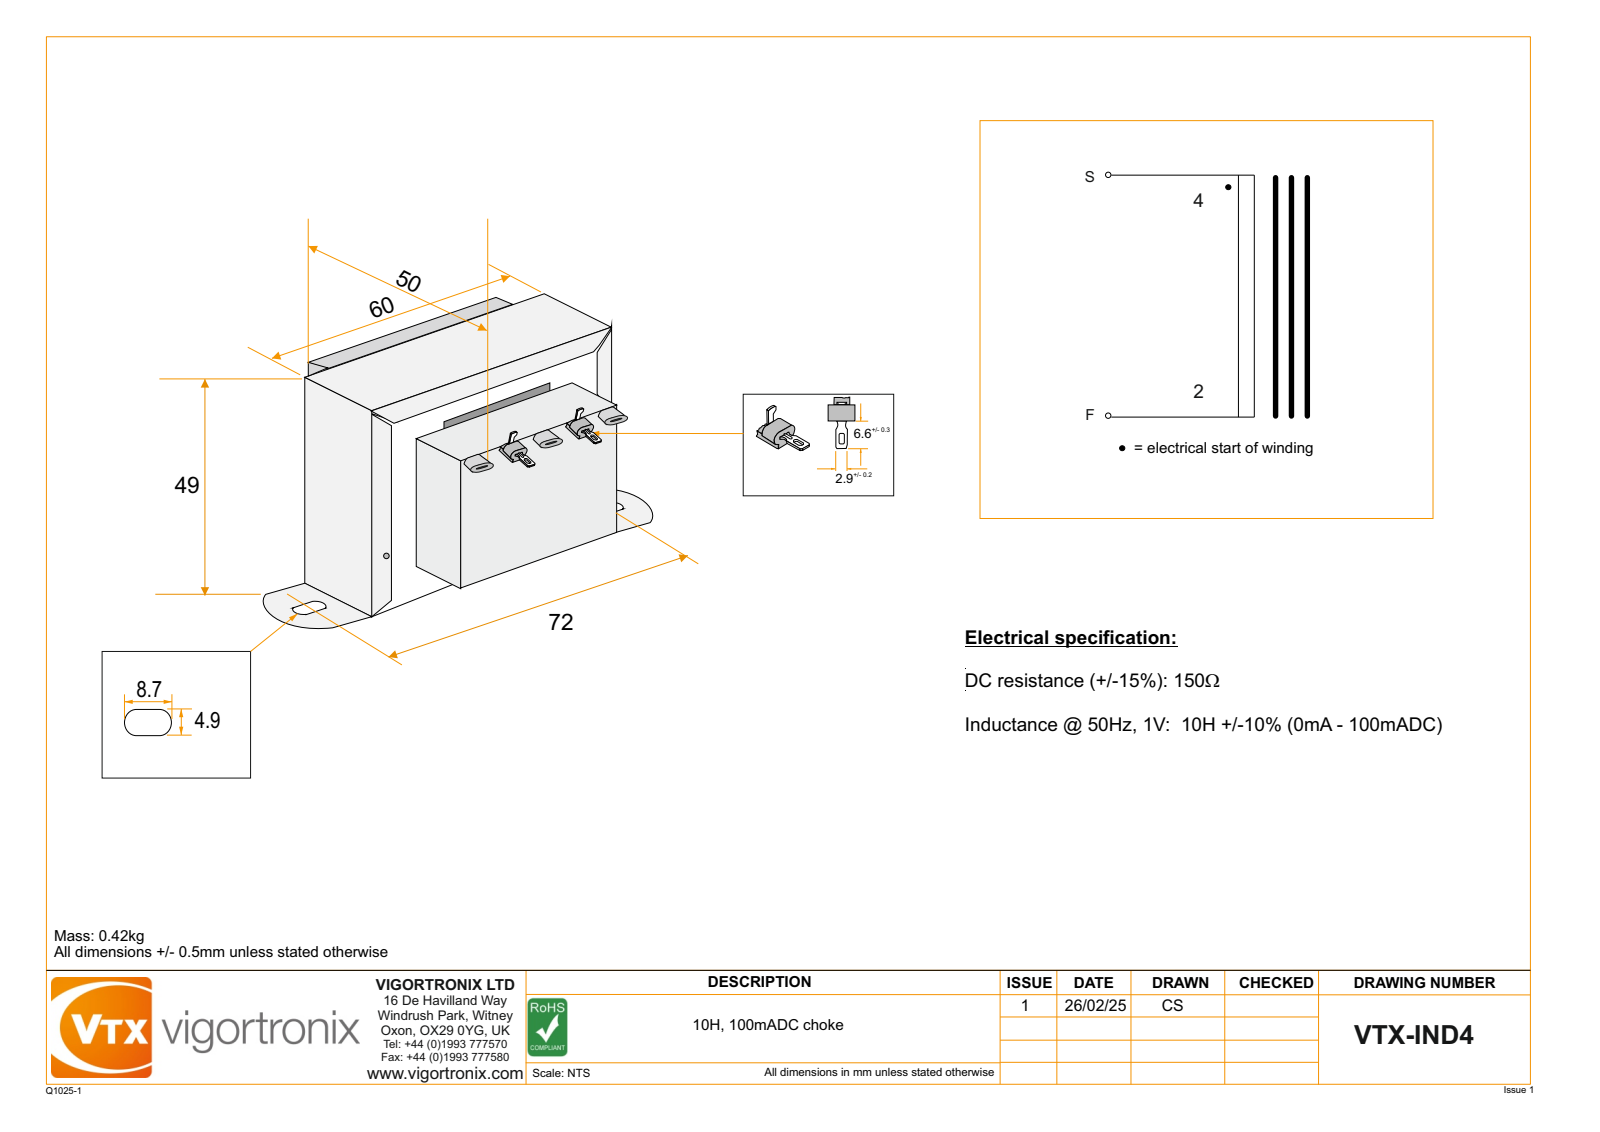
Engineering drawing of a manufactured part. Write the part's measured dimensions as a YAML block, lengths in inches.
part_name: "35 x 1 inch S02800 Bobbin; VTX-IND4; I UK35; Clamp EI UK35 Wide (+3 more)"
step_written_by: "SolidWorks 2024 (AUTOMOTIVE_DESIGN)"
units: inches
bodies: {solids: 133, faces: 1831, planar: 1684, cylindrical: 135, other: 12}
overall_size: [3.543, 2.22, 1.929]
volume: 5.044
surface_area: 499.2
partial_cylinders:
  - {radius: 0.039, count: 22}
  - {radius: 0.059, count: 20}
  - {radius: 0.025, count: 18}
  - {radius: 0.004, count: 12}
  - {radius: 0.071, count: 10}
  - {radius: 0.01, count: 5}
  - {radius: 0.096, count: 4}
  - {radius: 0.276, count: 4}
face_to_face_distances: [0.031, 0.063, 0.094, 0.126, 0.157, 0.189, 0.22, 0.252, 0.283, 0.315]
